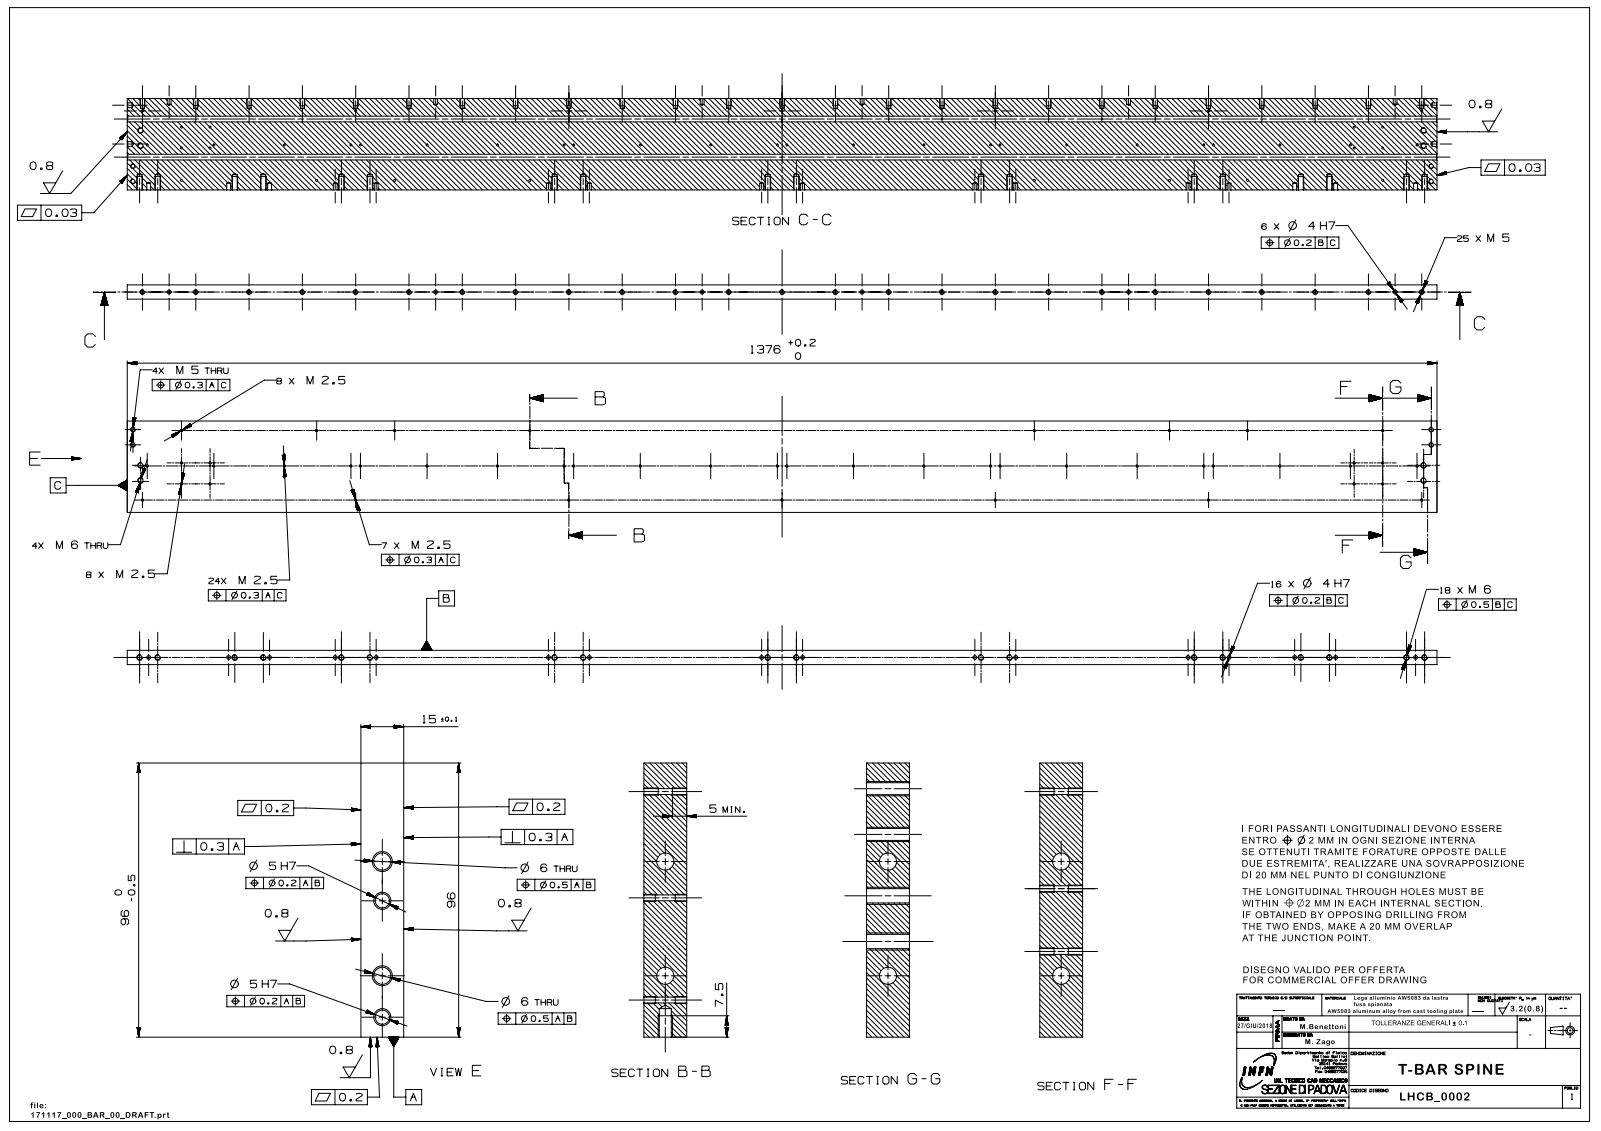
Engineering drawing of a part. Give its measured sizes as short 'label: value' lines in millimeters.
name: zago1E24C2460tt5
written by: SIEMENS PLM Software NX 11.0 (AP203_CONFIGURATION_CONTROLLED_3D_DESIGN_OF_MECHANICAL_PARTS_AND_ASSEMBLIES_MIM_LF)
unit: mm
bodies: 1 solid, 209 faces (6 planar, 126 cylindrical, 77 other)
size: 1376 × 96 × 15
volume: 1 887 000 mm³; area: 375 940 mm²
holes: 47× ⌀2.05, 29× ⌀4.2, 24× ⌀5, 22× ⌀4, 2× ⌀6
face distances: 15, 96, 1376
hole spacings: 224, 448, 672, 56, 112, 168, 280, 336
